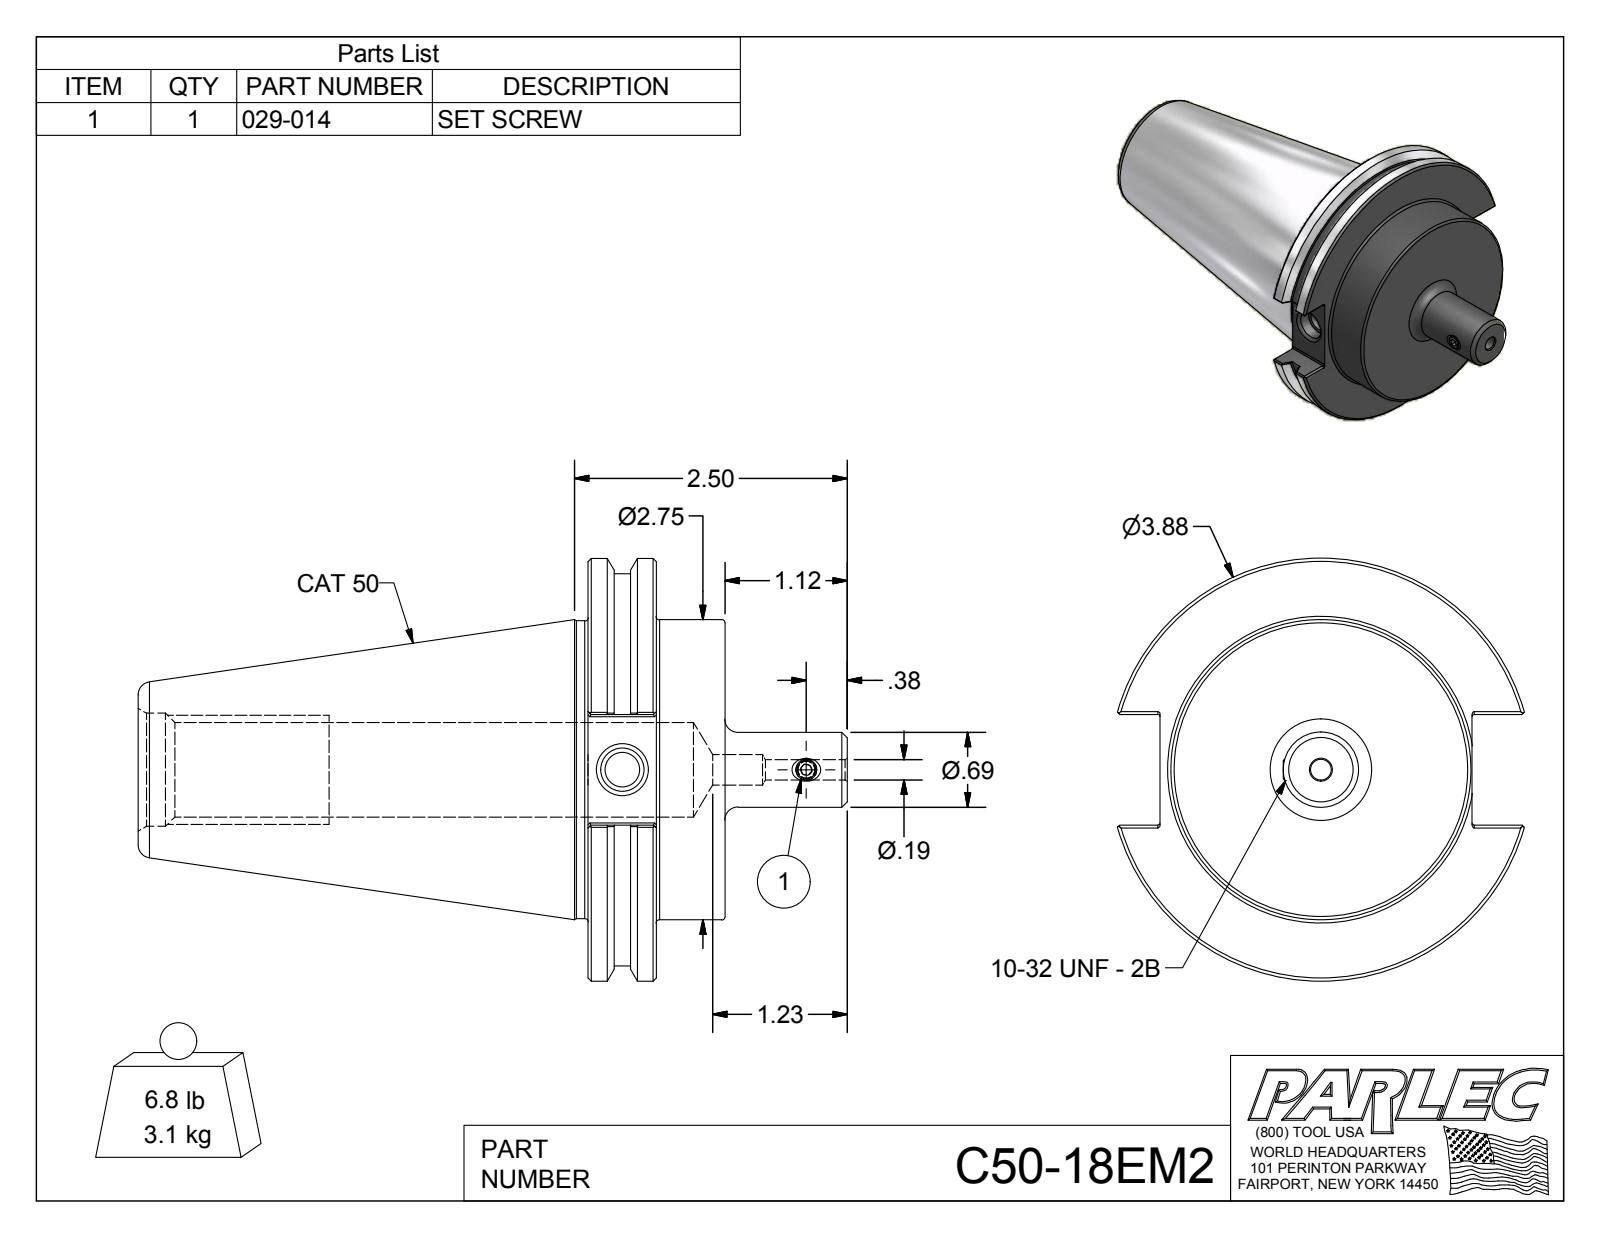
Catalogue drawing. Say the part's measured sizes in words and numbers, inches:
The part is named "C50-18EM2; C50-18EM2-1; 029-014". Its 3-D file was written by "Autodesk Inventor 2012 (AUTOMOTIVE_DESIGN)". It is 2 solids with 104 faces: 41 planar, 29 cylindrical and 34 other. Overall it measures 6.5 by 3.875 by 3.729 inches. Its volume is 23.23 cubic inches and its surface area 78.78 square inches. Round holes: 1 of diameter 0.159, 1 of diameter 0.187, 1 of diameter 0.28, 1 of diameter 0.315, 1 of diameter 0.399, 1 of diameter 0.865, 1 of diameter 1.038. Round bosses or shafts: 1 of diameter 3.875, 1 of diameter 3.594, 1 of diameter 2.75, 1 of diameter 2.73, 1 of diameter 0.687, 1 of diameter 0.19. Partial cylindrical surfaces (rounded edges, fillets, slot ends): 12 of radius 0.02. The main face-to-face distances are 1.255, 0.625, 0.63, 4.125, 4.75, 5.38, 2.86, 1.015, 4.363, 0.238. The hole center spacings are 1.685.
